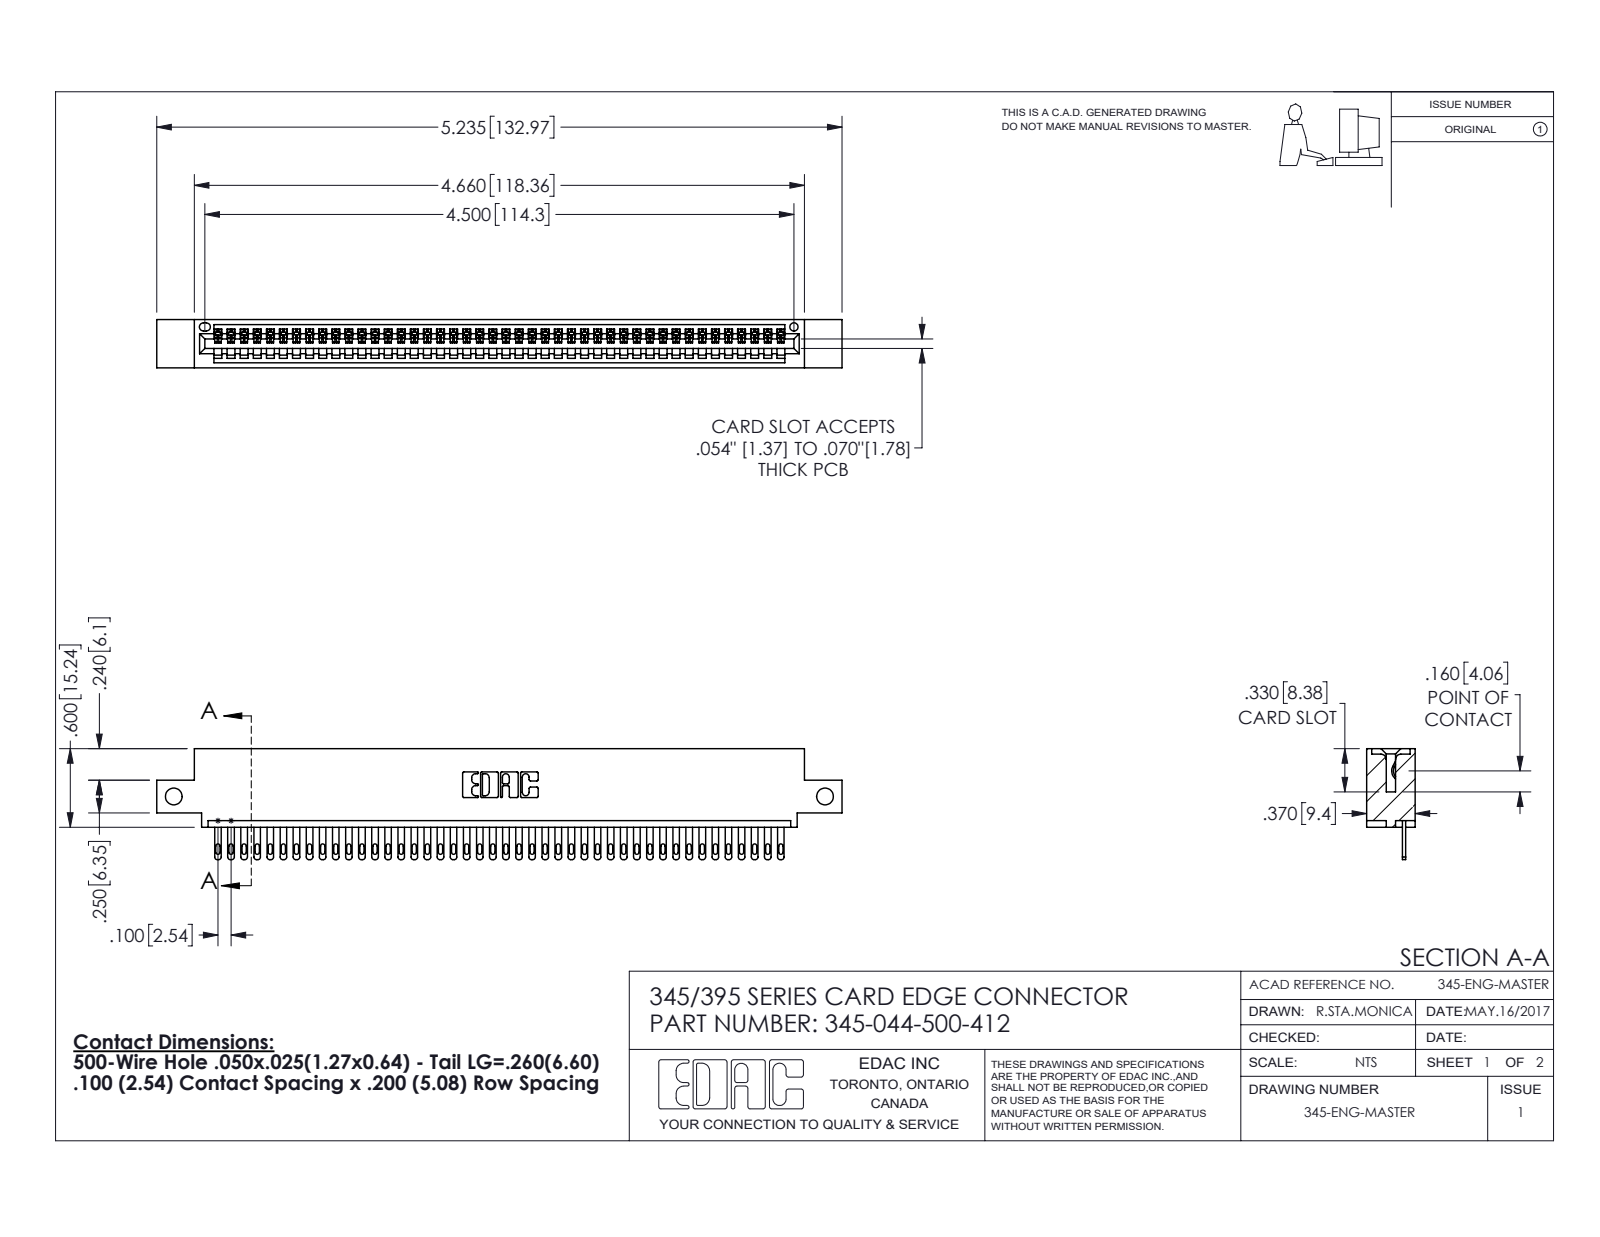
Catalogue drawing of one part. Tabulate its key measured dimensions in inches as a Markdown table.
| quantity | value |
| --- | --- |
| part name | 345-044-500-412; 345-292-001_345-293-100; 345 Part_0.110 Offset - Side Mount |
| STEP written by | SolidWorks 2016 (CONFIG_CONTROL_DESIGN) |
| units | inches |
| bodies | 45 solids, 2506 faces (1580 planar, 926 cylindrical, 0 other) |
| overall size | 5.235 × 0.847 × 0.37 |
| volume | 0.764 in³ |
| surface area | 25.88 in² |
| round holes (diameter × count) | 0.128 × 2, 0.064 × 1 |
| partial cylindrical surfaces (radius × count) | 0.006 × 88, 0.016 × 88, 0.02 × 88, 0.01 × 22, 0.007 × 6, 0.031 × 6, 0.026 × 3, 0.031 × 2 |
| main face-to-face distances | 0.298, 0.072, 0.37, 0.098, 0.272, 0.025, 0.2, 0.225, 0.149, 0.072 |
| hole center spacings | 4.975 |
